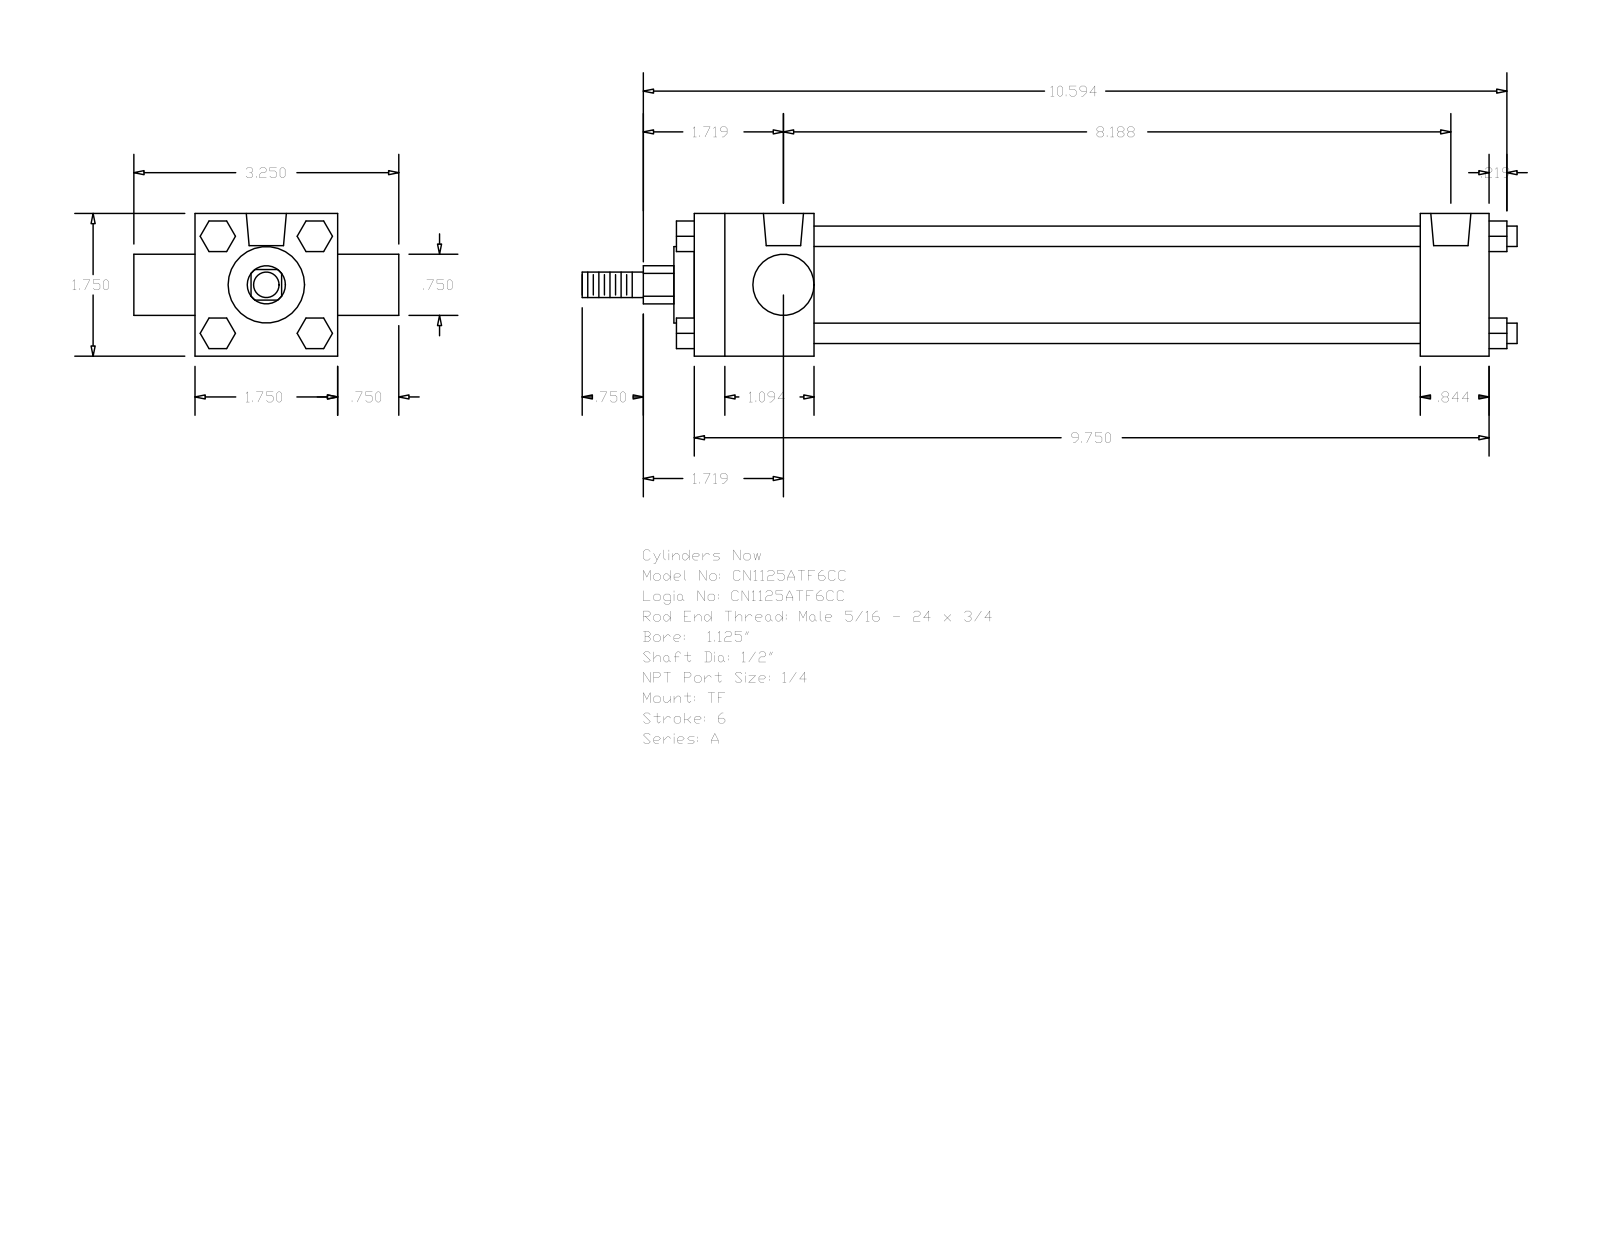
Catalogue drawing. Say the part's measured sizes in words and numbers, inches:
The part is named "A_TF__0112_0.5". Its 3-D file was written by "GSSL Pune (CONFIG_CONTROL_DESIGN)". It is 0 solids with 120 faces: 92 planar, 28 cylindrical and 0 other. Overall it measures 11.469 by 3.25 by 1.75 inches. Round holes: 3 of diameter 0.219, 2 of diameter 0.492. Round bosses or shafts: 4 of diameter 0.25, 1 of diameter 1.255, 1 of diameter 0.937, 1 of diameter 0.75, 1 of diameter 0.5, 1 of diameter 0.313. Partial cylindrical surfaces (rounded edges, fillets, slot ends): 1 of radius 0.234. The main face-to-face distances are 1.75, 9.75, 8.906, 0.844, 1.469, 7.437, 8.281, 0.75, 2.5, 0.375. The hole center spacings are 0.062, 0.063, 8.063, 8.125, 8.125, 8.187.
